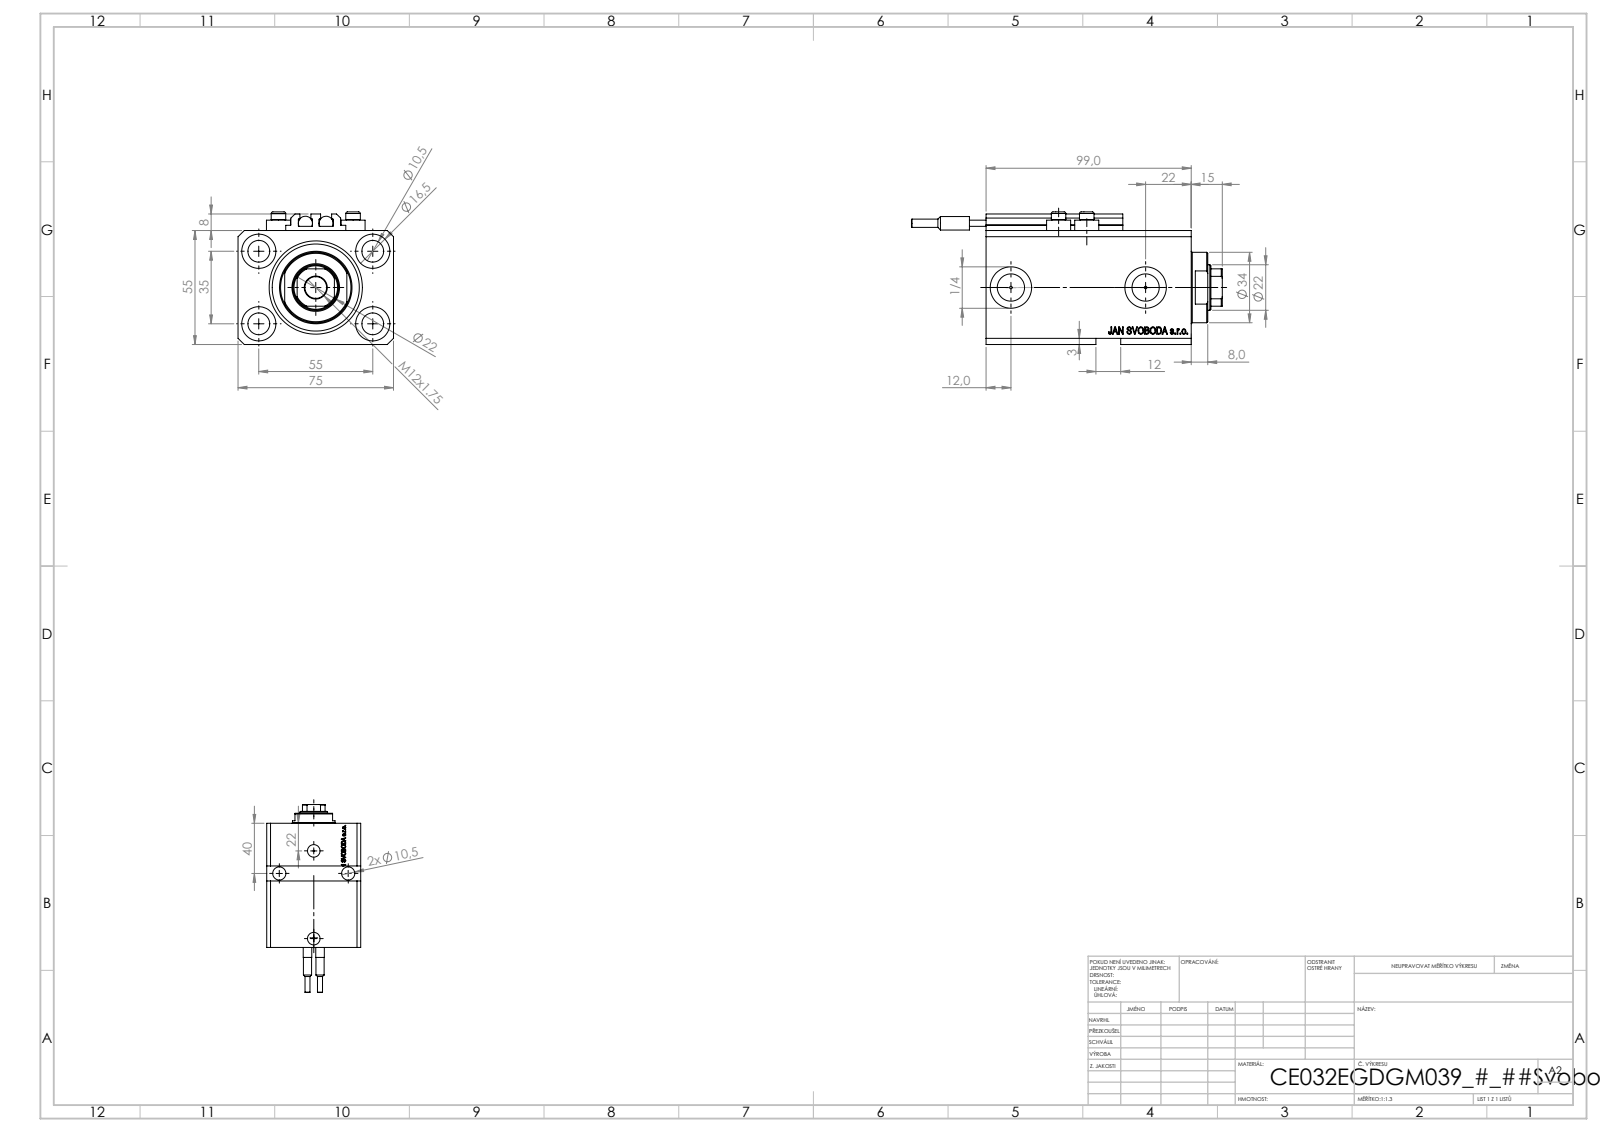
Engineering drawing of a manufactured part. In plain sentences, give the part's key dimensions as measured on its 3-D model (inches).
The part is named "V250CE_E_Body; SWITCH_V250CE; ALLEN BOLT V250CE; V250CE_C_VCP (+1 more)". Its 3-D file was written by "SolidWorks 2019 (CONFIG_CONTROL_DESIGN)". It is 10 solids with 1132 faces: 550 planar, 150 cylindrical and 432 other. Overall it measures 5.906 by 2.953 by 2.52 inches. Its volume is 21.34 cubic inches and its surface area 140.8 square inches. Round holes: 7 of diameter 0.413, 4 of diameter 0.049, 4 of diameter 0.157, 4 of diameter 0.65, 2 of diameter 0.394, 2 of diameter 0.518, 2 of diameter 0.787, 1 of diameter 0.866, 1 of diameter 1.26, 1 of diameter 1.772. Round bosses or shafts: 4 of diameter 0.457, 4 of diameter 0.276, 2 of diameter 0.268, 2 of diameter 0.256, 2 of diameter 0.157, 1 of diameter 1.339. Partial cylindrical surfaces (rounded edges, fillets, slot ends): 10 of radius 0.008, 1 of radius 0.413. The main face-to-face distances are 2.165, 2.953, 0.118, 0.591, 3.898, 3.307, 0.39, 2.244, 2.126, 2.917. The hole center spacings are 1.283, 2.165, 0.535, 0.555, 1.016, 1.293, 1.294, 1.311.
